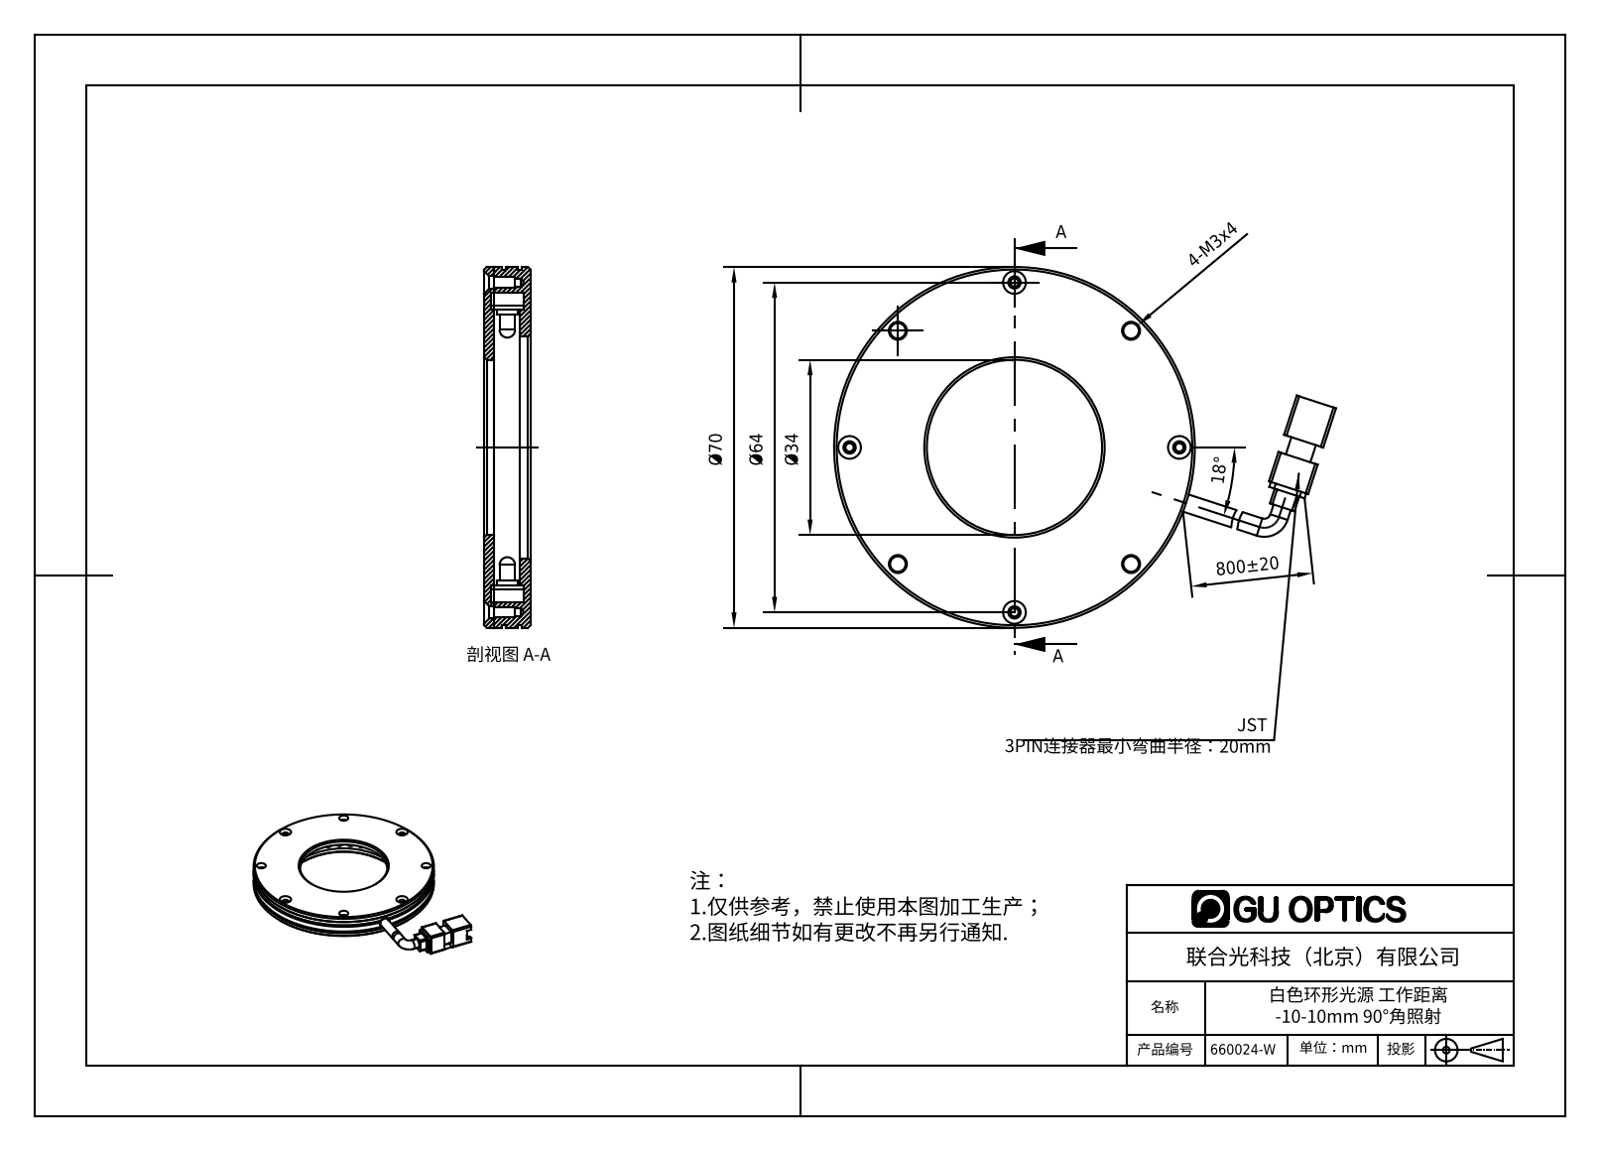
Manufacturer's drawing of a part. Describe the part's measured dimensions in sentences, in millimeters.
The part is named "660024-W". Its 3-D file was written by "SolidWorks 2016 (AUTOMOTIVE_DESIGN)". It is 37 solids with 771 faces: 464 planar, 242 cylindrical and 65 other. Overall it measures 97.4 by 70 by 11 millimeters. Its volume is 17 278 cubic millimeters and its surface area 21 297 square millimeters. Round holes: 4 of diameter 1.6, 4 of diameter 2, 4 of diameter 2.4, 4 of diameter 3, 4 of diameter 3.5, 1 of diameter 3.6, 1 of diameter 3.8, 1 of diameter 34, 1 of diameter 43, 1 of diameter 54, 1 of diameter 60. Round bosses or shafts: 32 of diameter 3, 31 of diameter 3.8, 2 of diameter 3.5, 1 of diameter 70, 1 of diameter 69, 1 of diameter 54.8, 1 of diameter 53.6. Partial cylindrical surfaces (rounded edges, fillets, slot ends): 8 of radius 0.5, 4 of radius 1, 2 of radius 1.5, 1 of radius 33. The main face-to-face distances are 2, 7, 9, 0.6, 7.6, 5.6, 1.4, 5, 6.2, 1. The hole center spacings are 24.49, 32, 59.13, 45.25, 45.26, 64, 64.01.
